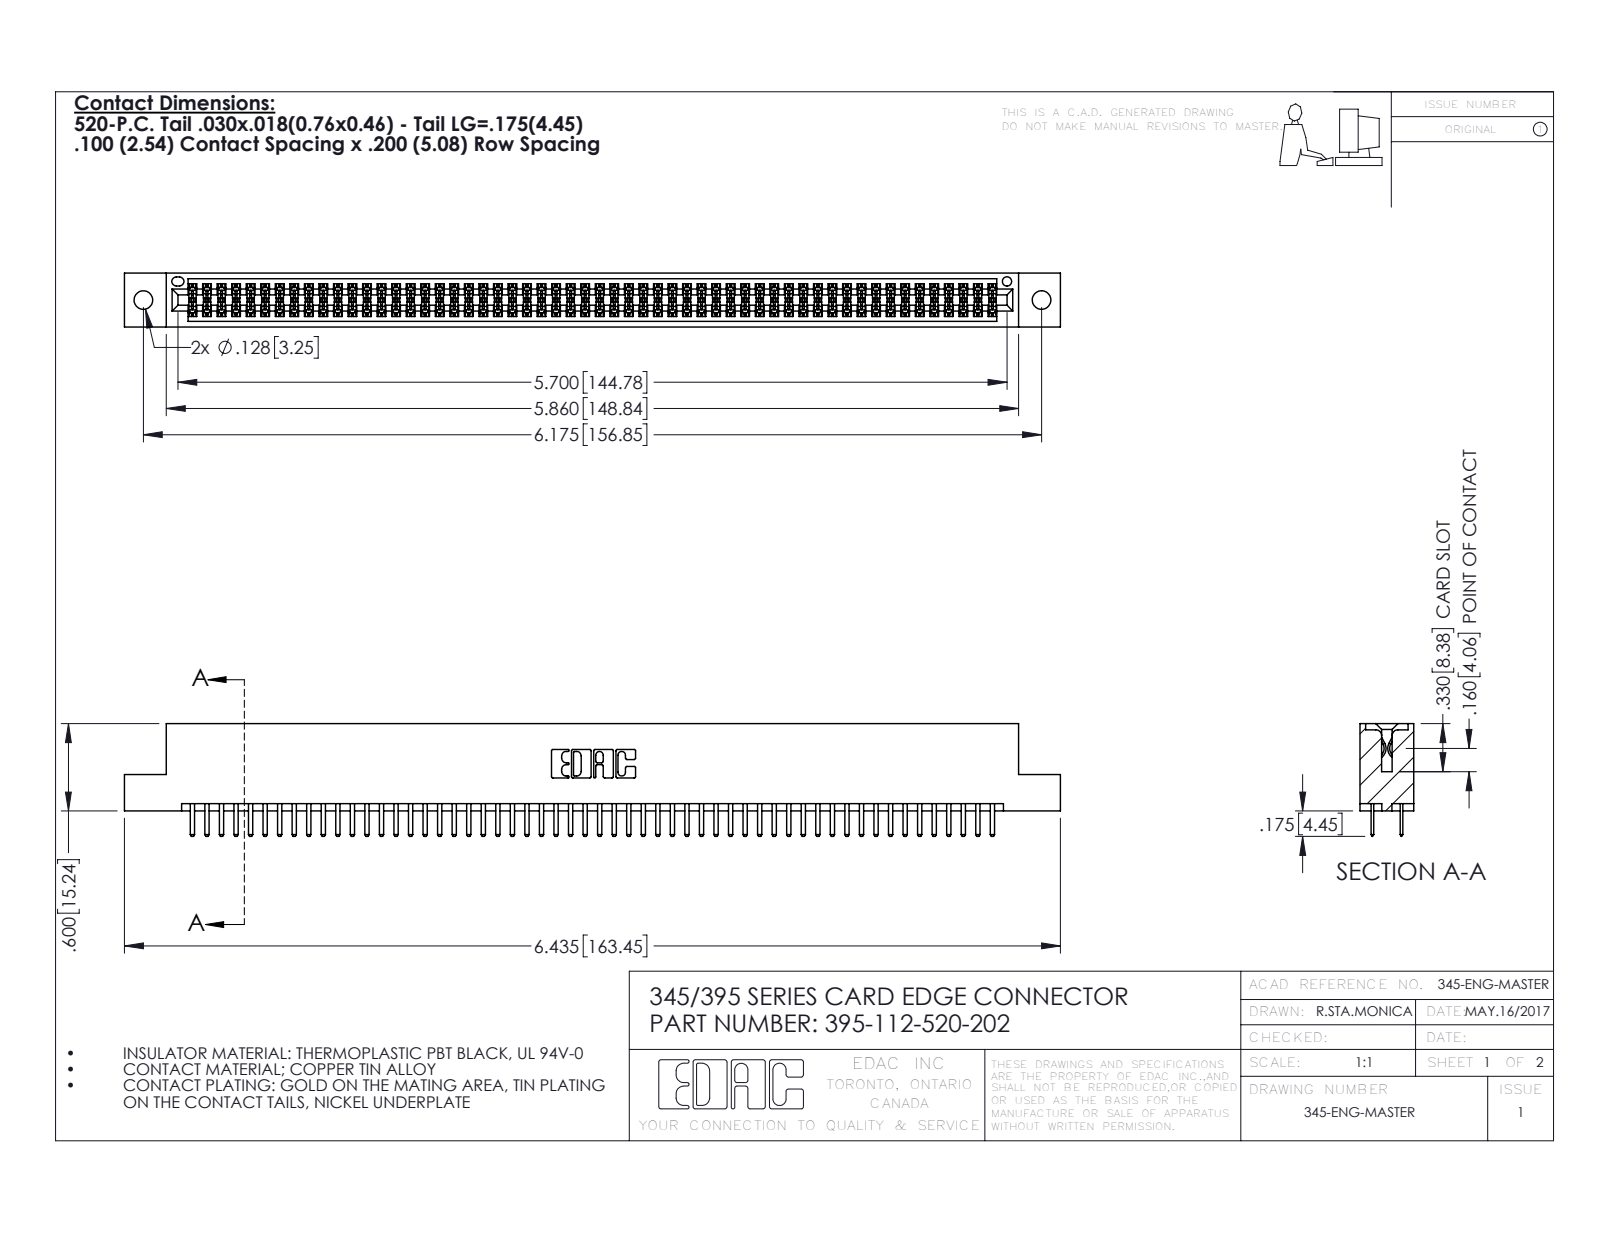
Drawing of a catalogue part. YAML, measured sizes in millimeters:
part_name: "395-112-520-202; 345 Part_Flush Mounting Lugs - 0.128 Dia; 345-292-001_345-293-120"
step_written_by: "SolidWorks 2016 (CONFIG_CONTROL_DESIGN)"
units: millimeters
bodies: {solids: 113, faces: 6174, planar: 4000, cylindrical: 2174, other: 0}
overall_size: [163.4, 19.7, 9.4]
volume: 15900
surface_area: 23430
round_holes:
  - {diameter: 3.3, count: 2}
  - {diameter: 1.6, count: 1}
partial_cylinders:
  - {radius: 0.2, count: 168}
  - {radius: 0.3, count: 116}
  - {radius: 0.3, count: 22}
  - {radius: 0.2, count: 6}
  - {radius: 0.8, count: 6}
  - {radius: 0.7, count: 3}
  - {radius: 0.4, count: 2}
  - {radius: 0.5, count: 2}
face_to_face_distances: [7.6, 1.8, 5.1, 9.4, 2.5, 6.9, 0.6, 5.7, 0.6, 1.8]
hole_center_spacings: [6.9, 150.9, 156.8]
